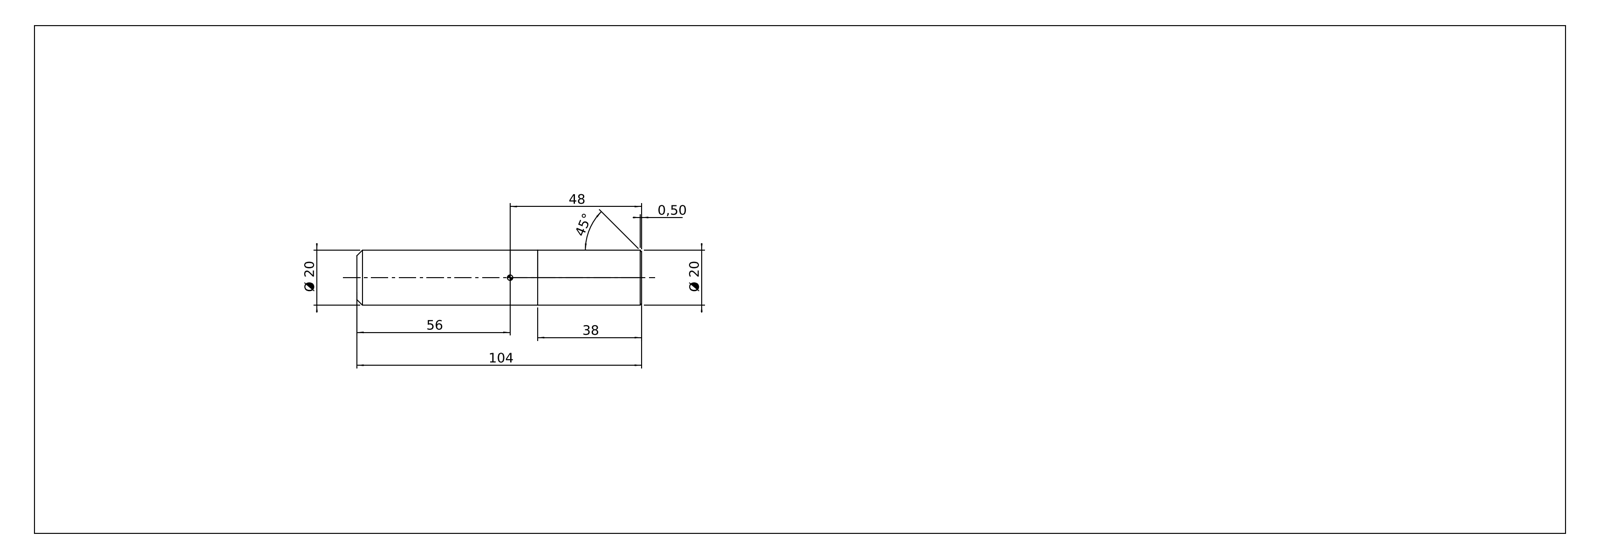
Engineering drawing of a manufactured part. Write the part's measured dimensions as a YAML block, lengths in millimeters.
part_name: "727.200.00"
step_written_by: "SolidWorks 2019 (CONFIG_CONTROL_DESIGN)"
units: millimeters
bodies: {solids: 2, faces: 8, planar: 4, cylindrical: 2, other: 2}
overall_size: [104, 20, 20]
volume: 32548
surface_area: 7694
round_bosses_or_shafts:
  - {diameter: 20, count: 1}
face_to_face_distances: [38, 104, 66]
